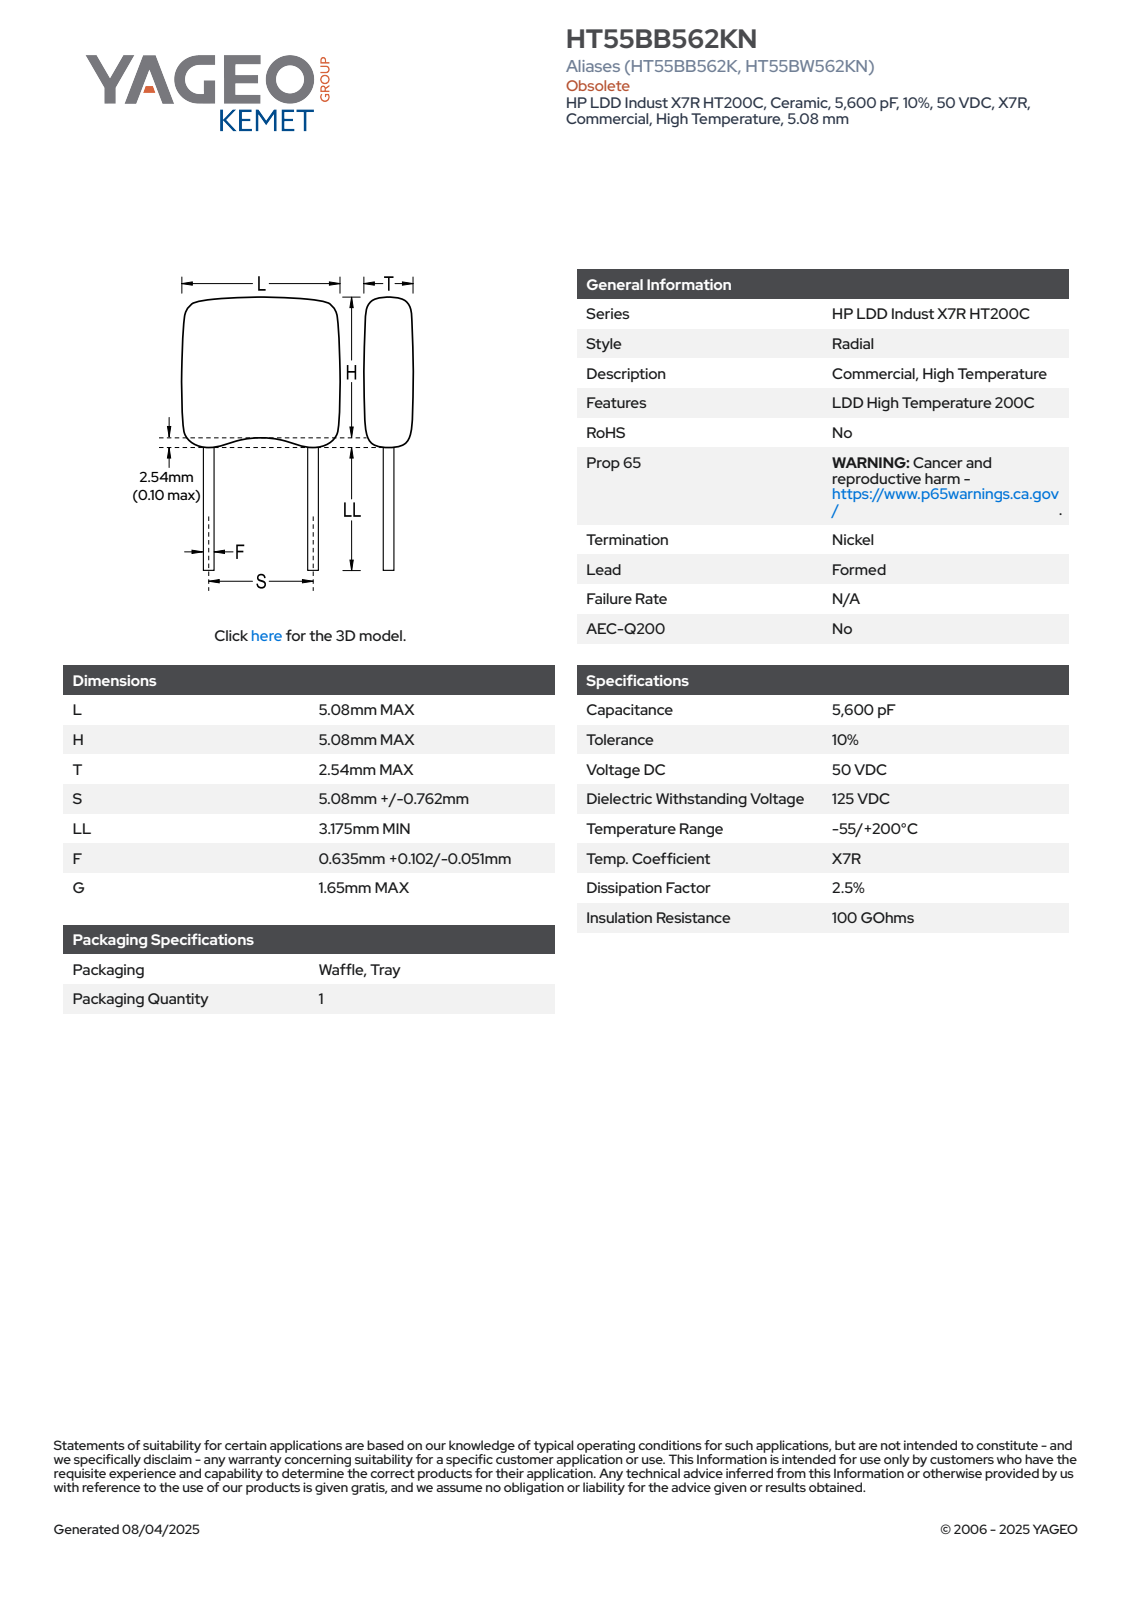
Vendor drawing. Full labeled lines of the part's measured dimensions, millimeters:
Part name (STEP PRODUCT): CCR_RCST2_HT55_L5.08H5.08T2.54S5.08LL3.175F0.737
STEP written by: SolidWorks 2021 (AUTOMOTIVE_DESIGN)
Units: millimetres
Bodies: 4 solids, 96 faces (64 planar, 16 cylindrical, 16 other)
Overall size (bounding box): 10.79 × 5.08 × 2.54
Volume: 75 mm³ · Surface area: 131 mm²
Round bosses / shafts (diameter × count): ⌀0.74 ×2
Partial cylindrical surfaces — rounded edges, fillets, slot ends (radius × count): R1 ×10
Main face-to-face distances: 2.54, 5.08, 10.79, 7.97, 2.82, 7.28, 0.69, 3.51, 0.56, 2.85
